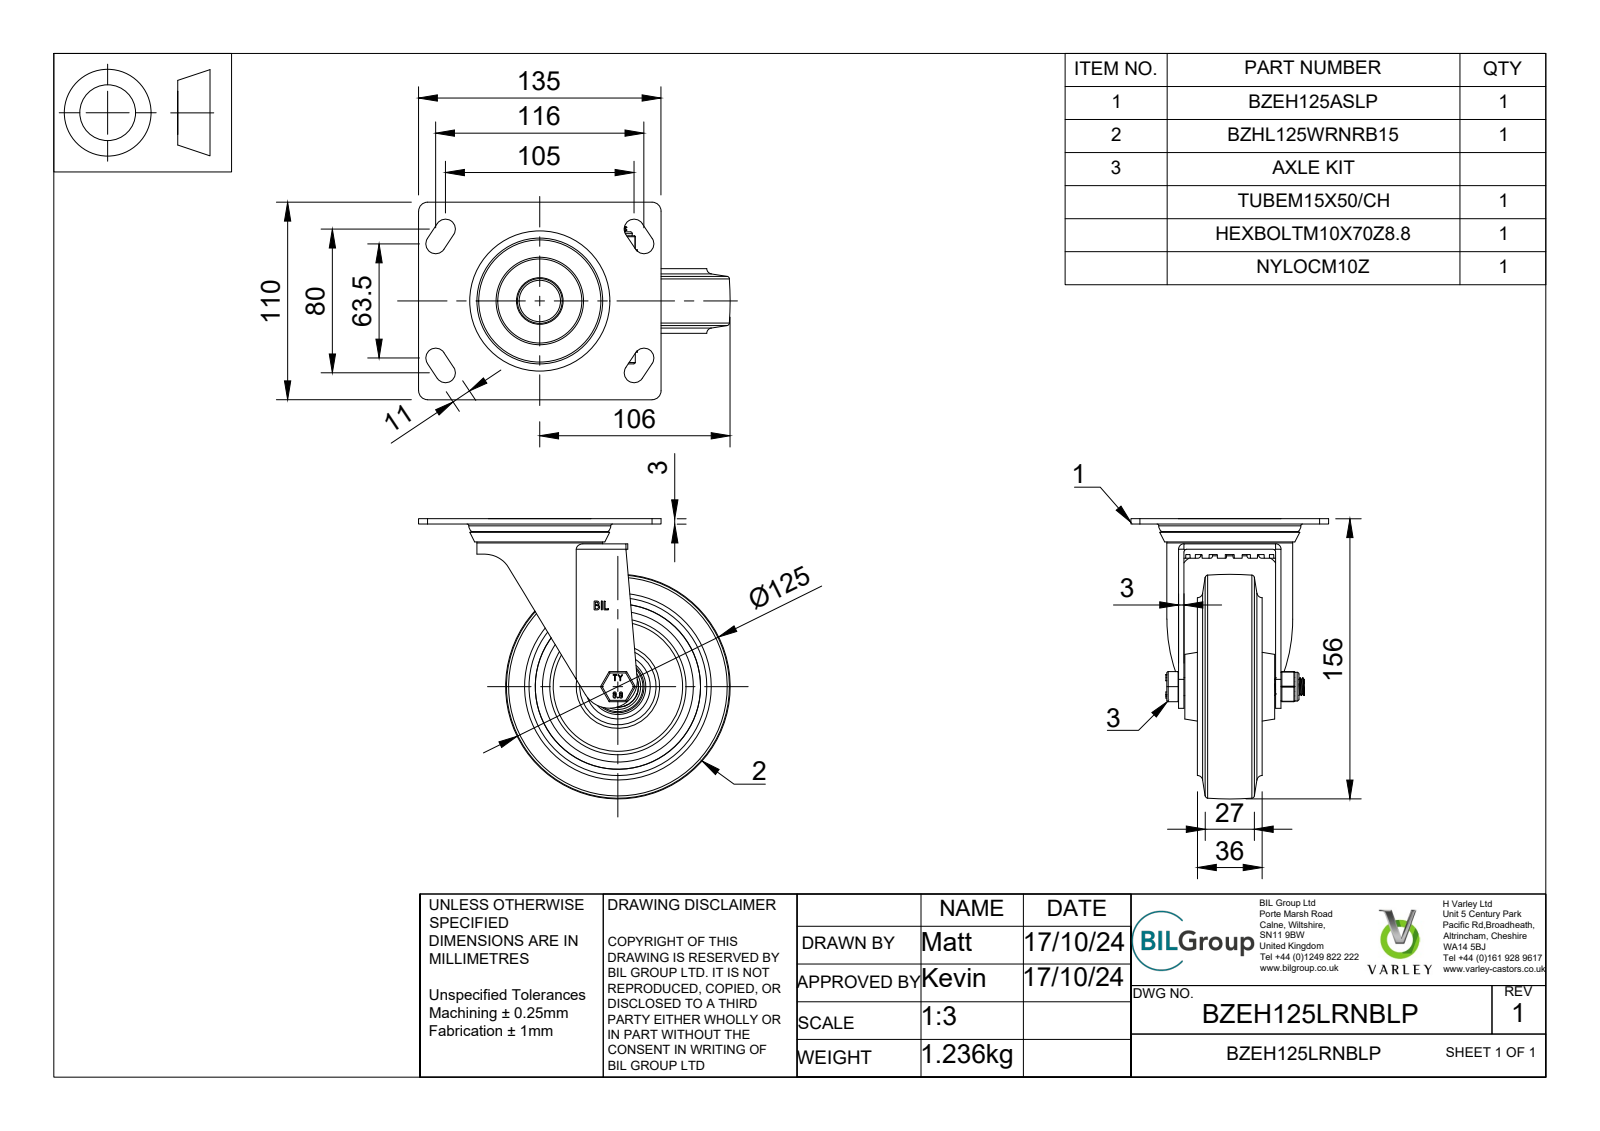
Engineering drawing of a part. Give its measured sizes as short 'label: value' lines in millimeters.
name: BZEH125LRNBLP v3; BZEH125ASLP v1; ZINC PLATED, PRESSED STEEL TOP PLATE; ZINC PLATED, PRESSED STEEL TOP PLATE Geometry (+7 more)
written by: Autodesk Translation Framework v13.20.0.188 (AUTOMOTIVE_DESIGN)
unit: mm
bodies: 38 solids, 588 faces (303 planar, 143 cylindrical, 142 other)
size: 173.5 × 156 × 110
volume: 426 678 mm³; area: 161 631 mm²
holes: 1× ⌀10, 1× ⌀10.25, 1× ⌀10.5, 1× ⌀12, 1× ⌀15, 1× ⌀23, 1× ⌀31, 1× ⌀34, 1× ⌀44.58, 1× ⌀64, 1× ⌀92
bosses: 8× ⌀4, 2× ⌀16, 1× ⌀70, 1× ⌀54, 1× ⌀25, 1× ⌀22.75, 1× ⌀21, 1× ⌀10
rounds: 18× R0.5, 8× R5.5, 6× R0.75, 4× R1.5, 4× R5, 2× R3, 1× R9.38, 1× R15
face distances: 3, 10.5, 7.5, 21.5, 7, 54, 25, 22, 32, 29
